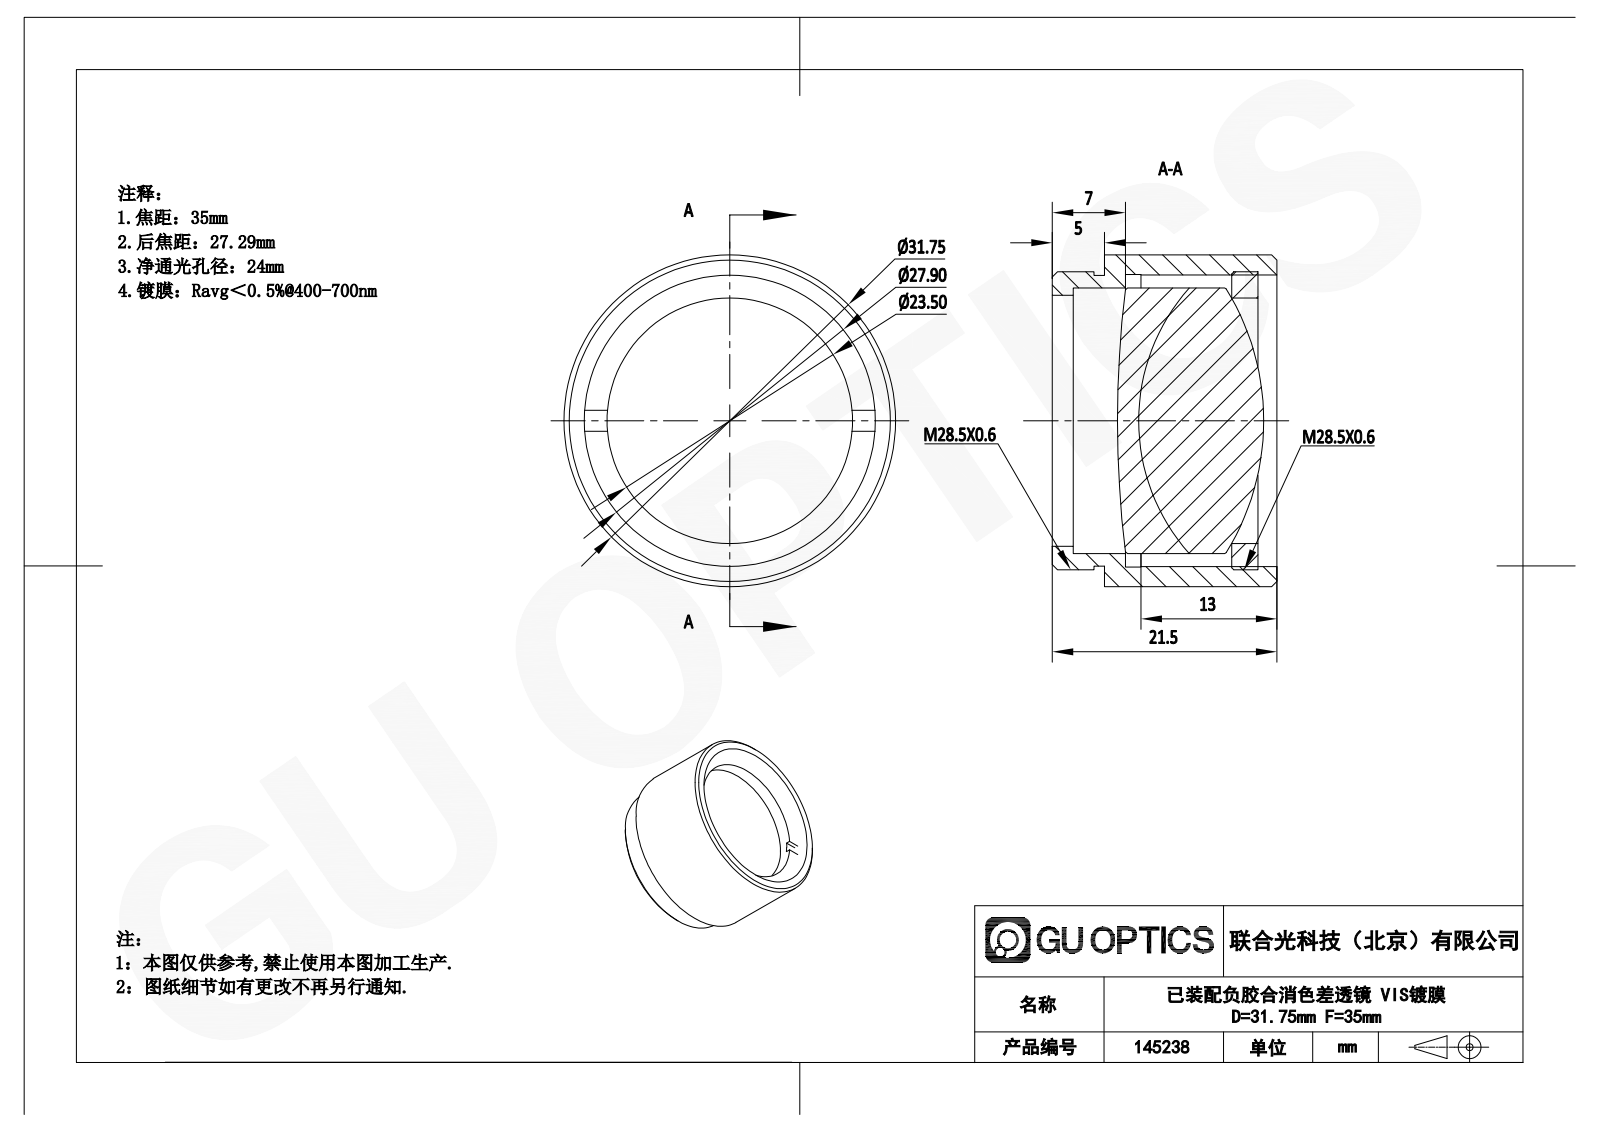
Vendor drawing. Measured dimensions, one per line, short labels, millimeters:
name: GL31-025B-035-VIS_Solidworks; APD-ML25-035-VIS; M28.5x0.6ѹȦ
written by: SolidWorks 2022 (AUTOMOTIVE_DESIGN)
unit: mm
bodies: 4 solids, 56 faces (16 planar, 22 cylindrical, 18 other)
size: 31.76 × 31.76 × 21.5
volume: 10 400 mm³; area: 8 388 mm²
holes: 1× ⌀23.5, 1× ⌀24, 1× ⌀27.9, 1× ⌀28
bosses: 1× ⌀31.76, 1× ⌀28.5, 1× ⌀27.8, 1× ⌀25.4
face distances: 2, 5, 2.5, 12.18, 14.68, 17.18, 19.68, 21.5, 16.5, 4.32
